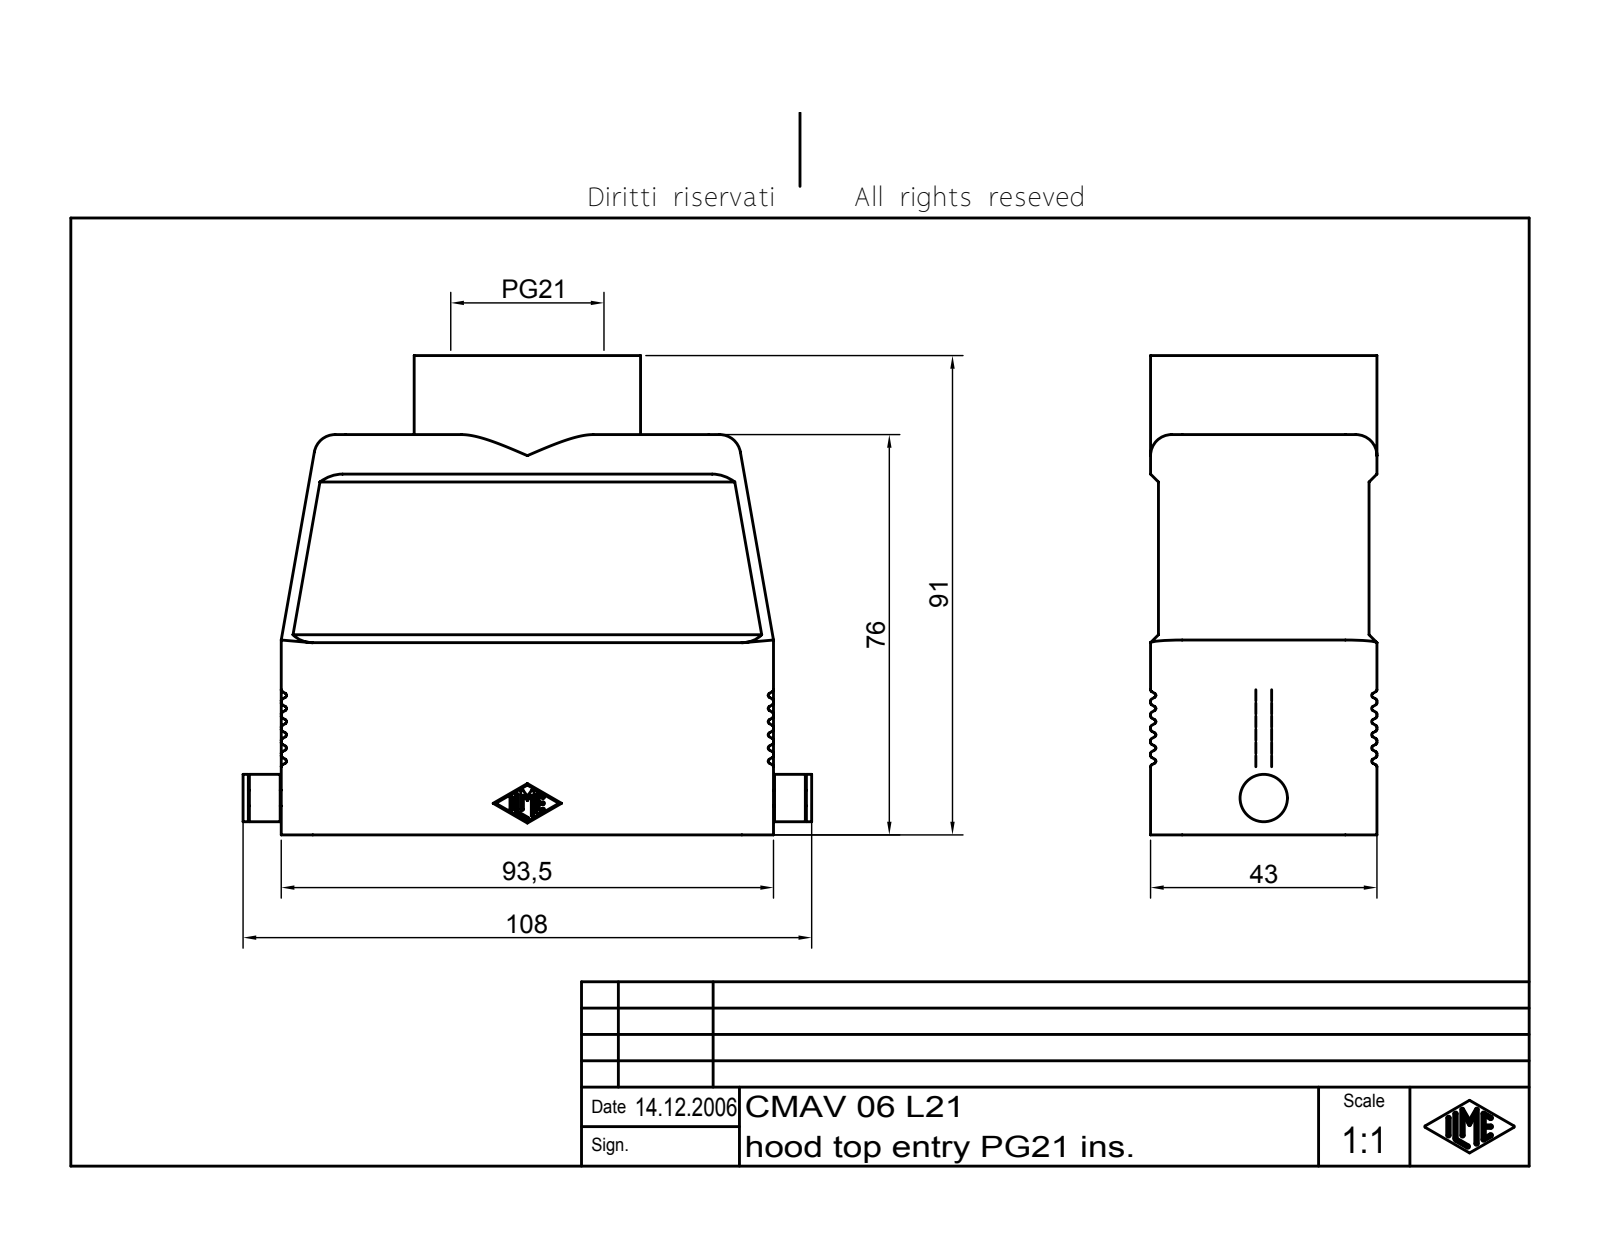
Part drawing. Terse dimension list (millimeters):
name: CMAV 06 L21
written by: Autodesk Inventor 7 (AUTOMOTIVE_DESIGN)
unit: mm
bodies: 1 solid, 843 faces (150 planar, 420 cylindrical, 273 other)
size: 108 × 91 × 43
volume: 80 749 mm³; area: 49 184 mm²
holes: 1× ⌀25, 1× ⌀26.78
bosses: 1× ⌀43, 1× ⌀9, 1× ⌀3
rounds: 96× R0.4, 14× R0.25, 8× R6, 4× R1.5, 4× R3, 4× R4, 2× R5
face distances: 1.5, 3, 40, 37, 38.5, 41.5, 43, 90.5, 18, 15
